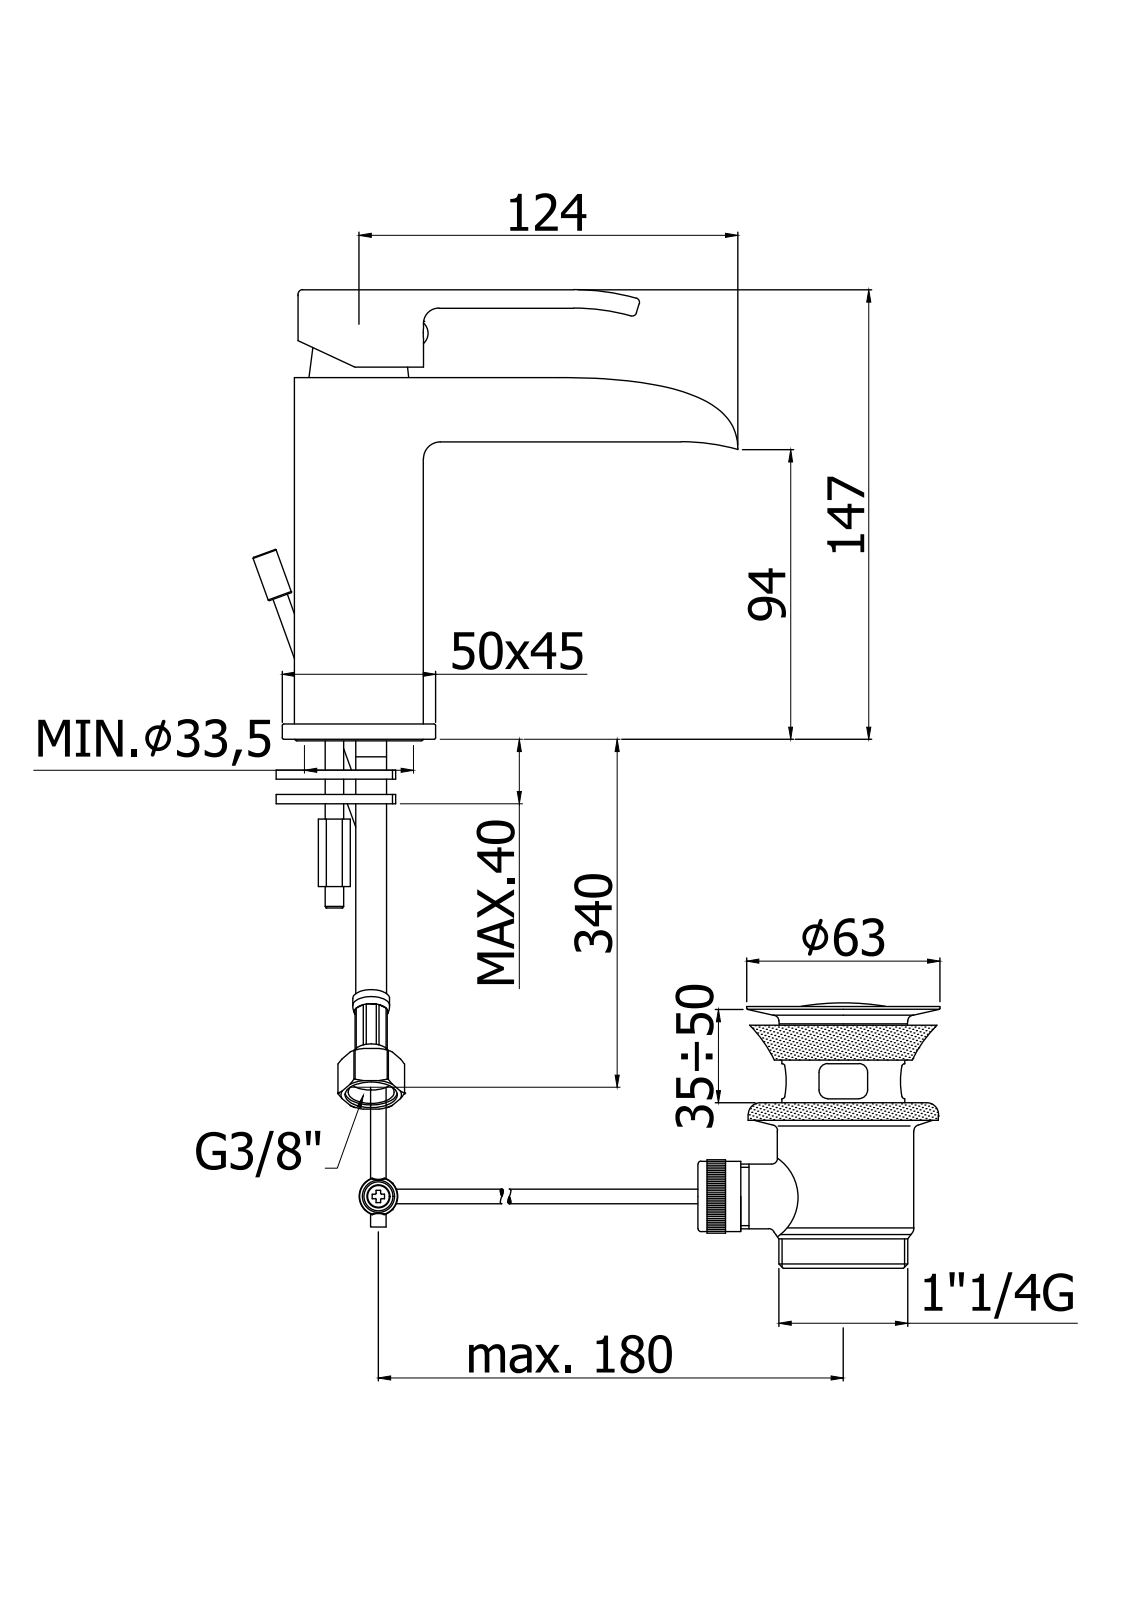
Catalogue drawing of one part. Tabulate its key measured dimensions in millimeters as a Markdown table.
| quantity | value |
| --- | --- |
| part name | LES065CR |
| STEP written by | CREO PARAMETRIC BY PTC INC, 2020044 (CONFIG_CONTROL_DESIGN) |
| units | millimeters |
| bodies | 3 solids, 1205 faces (342 planar, 454 cylindrical, 409 other) |
| overall size | 161.62 × 145.73 × 45 |
| volume | 165 976 mm³ |
| surface area | 93 889 mm² |
| round holes (diameter × count) | 2.5 × 6, 5 × 6, 5.5 × 4, 6.2 × 2, 7 × 2, 8.6 × 2, 9.4 × 2, 3 × 1, 7.8 × 1, 16.7 × 1, 19.2 × 1, 20.2 × 1 |
| round bosses / shafts (diameter × count) | 4 × 3, 38.8 × 1, 32 × 1, 31.5 × 1, 29.5 × 1, 28 × 1, 25.5 × 1, 25 × 1 |
| partial cylindrical surfaces (radius × count) | 0.5 × 59, 1.5 × 59, 2 × 18, 1 × 14, 0.7 × 10, 0.8 × 6, 4 × 6, 0.25 × 4 |
| main face-to-face distances | 38, 0.5, 35, 3.5, 1.5, 3, 34.5, 31.5, 3.75, 39.25 |
| hole center spacings | 13, 6.73, 10.55, 10.96, 0.75, 5.6, 6.28, 6.8 |
